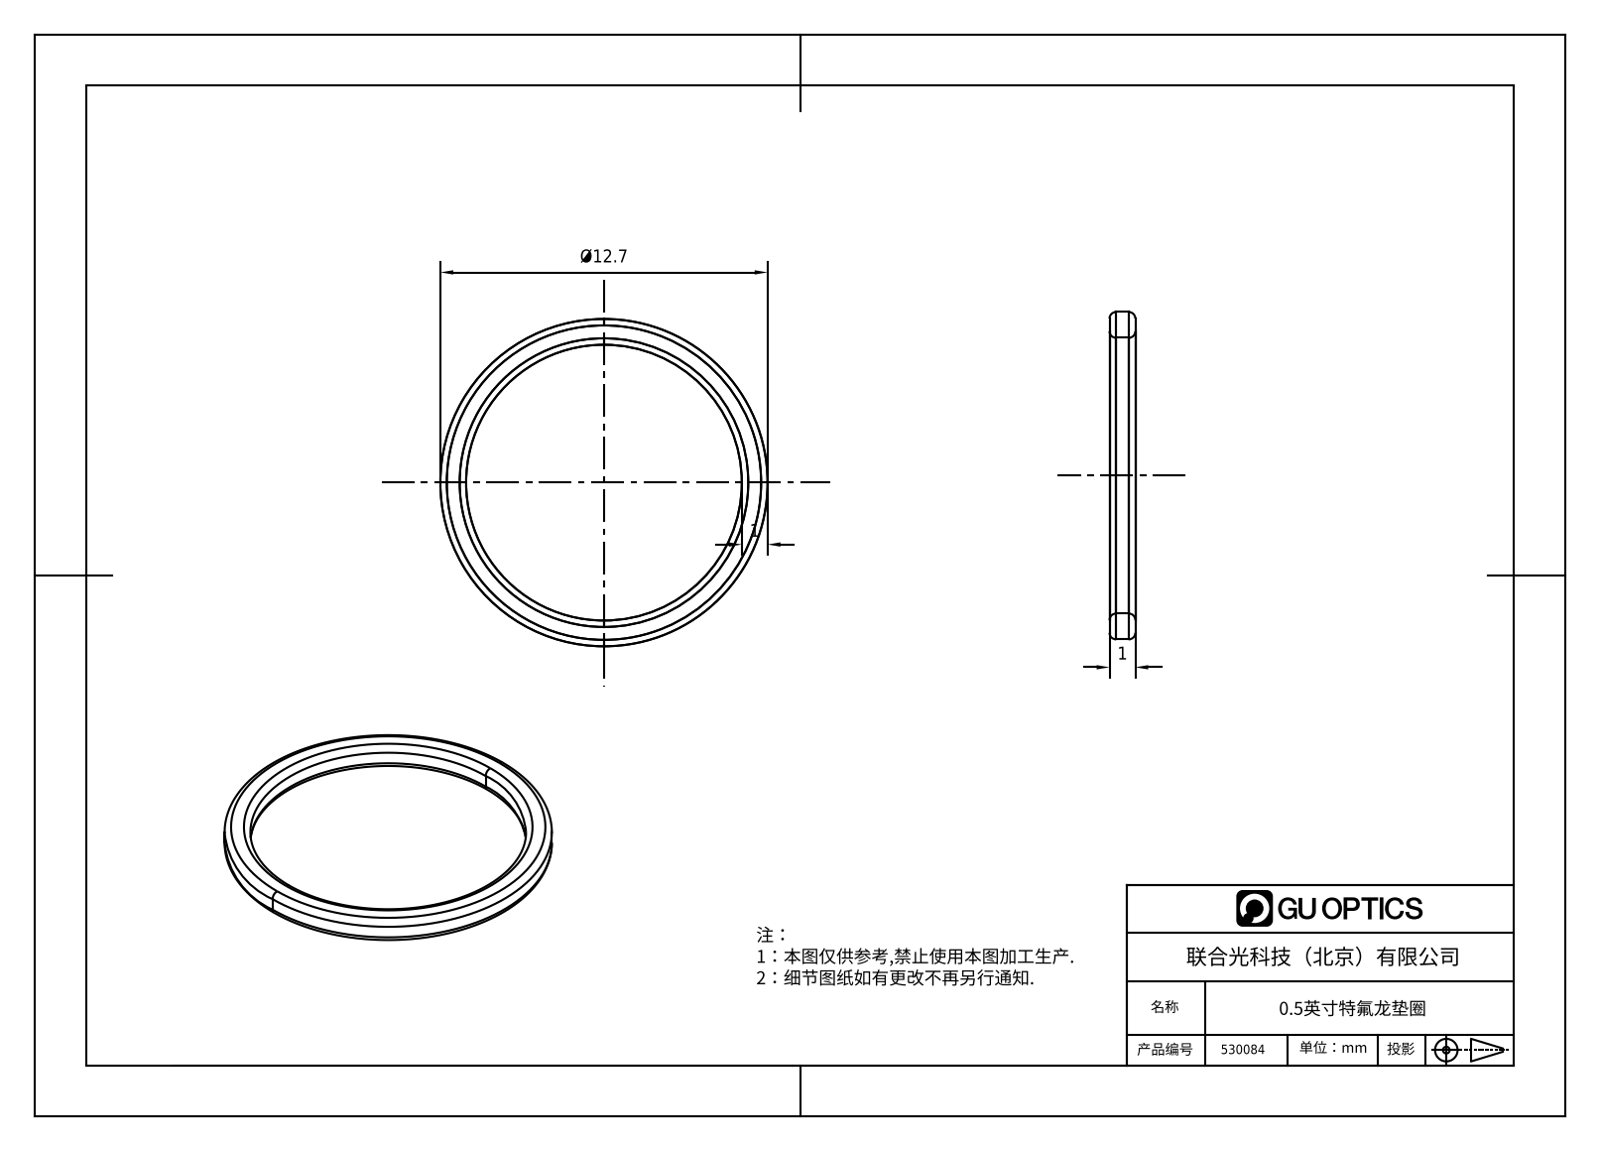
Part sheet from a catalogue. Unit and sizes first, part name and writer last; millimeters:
Units: millimetres
Overall size (bounding box): 12.7 × 12.7 × 1
Round holes (diameter × count): ⌀10.7 ×1
Round bosses / shafts (diameter × count): ⌀12.7 ×1
Main face-to-face distances: 1
Volume: 35 mm³ · Surface area: 131 mm²
Bodies: 1 solid, 14 faces (2 planar, 4 cylindrical, 8 other)
Part name (STEP PRODUCT): 1.8.5.23_ZFK-D0.5_0.5英寸特氟龙垫圈
STEP written by: SolidWorks 2018 (CONFIG_CONTROL_DESIGN)
